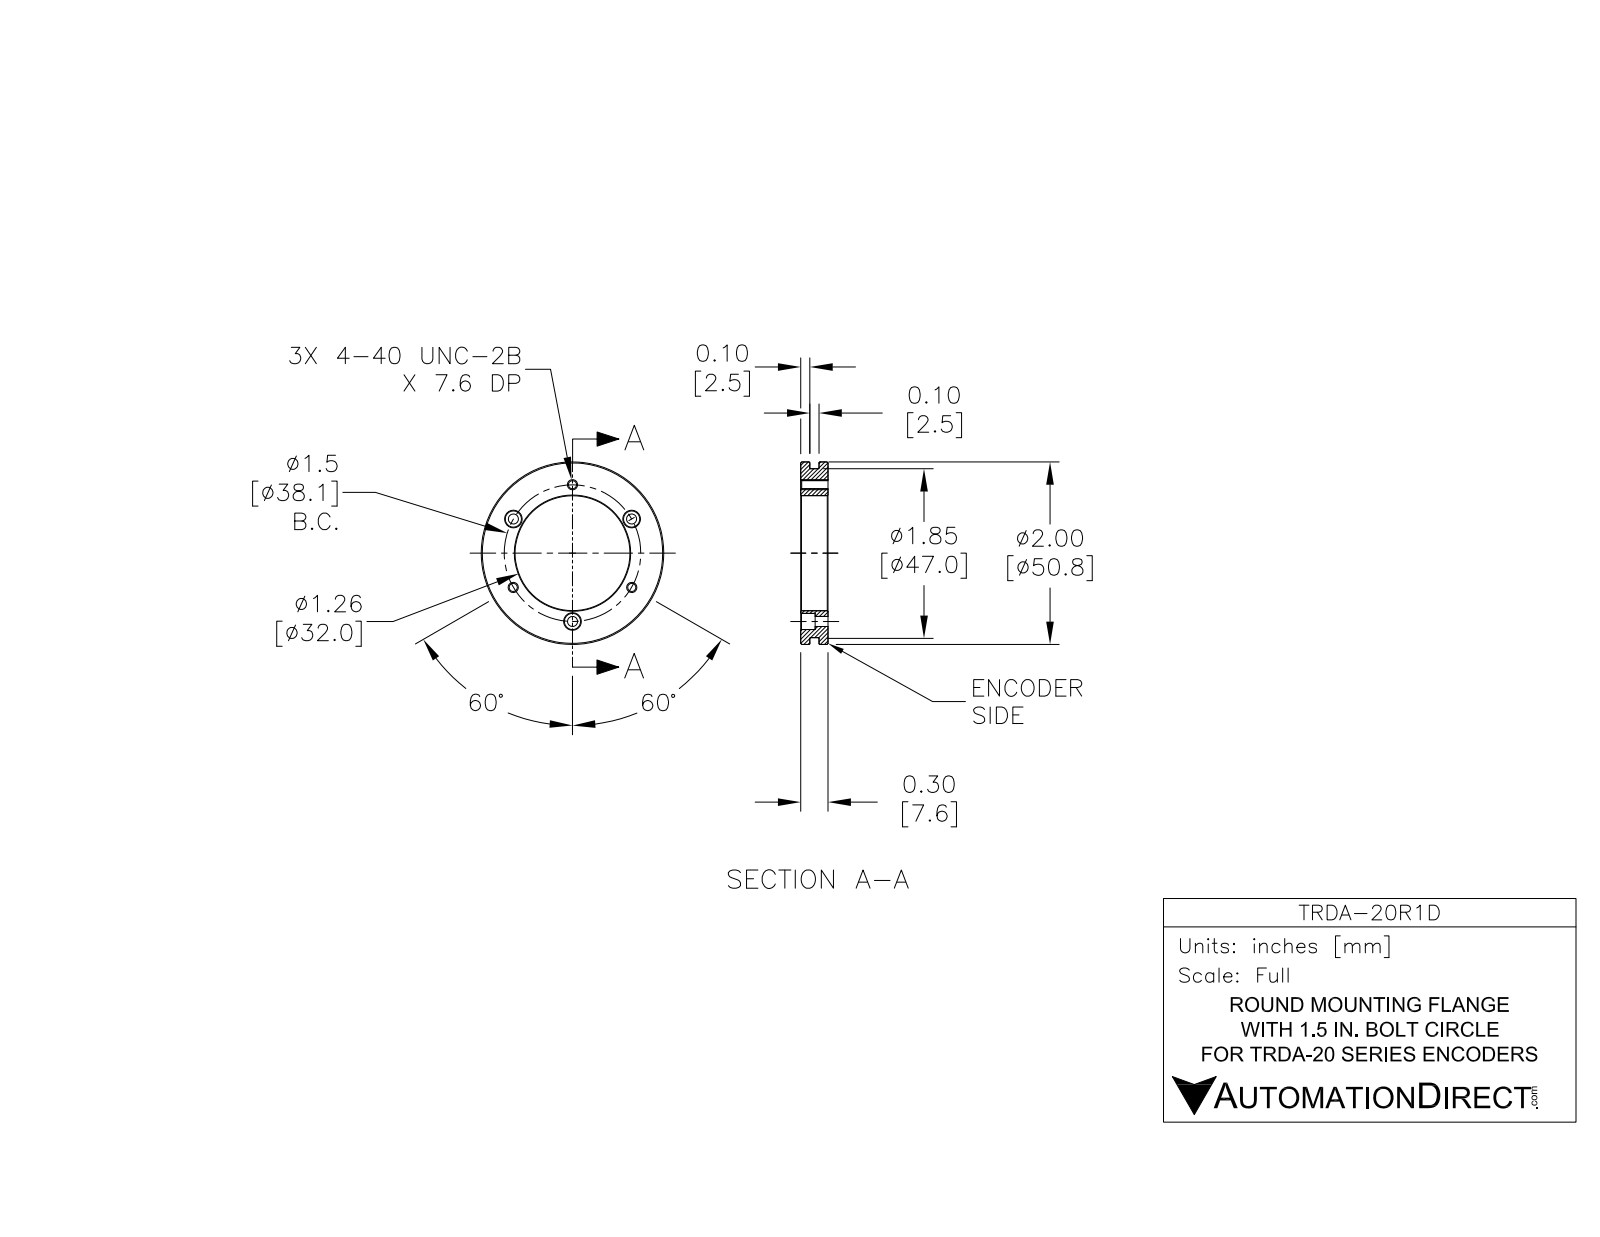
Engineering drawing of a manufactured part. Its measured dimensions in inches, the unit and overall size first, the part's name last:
Units: inches
Overall size (bounding box): 2 × 2 × 0.299
Round holes (diameter × count): ⌀0.089 ×3, ⌀0.11 ×3, ⌀0.177 ×3, ⌀1.26 ×1
Round bosses / shafts (diameter × count): ⌀0.11 ×3, ⌀2 ×1, ⌀1.85 ×1
Main face-to-face distances: 0.299, 0.1, 0.199, 0.099, 0.2, 0.142, 0.043, 0.057, 0.157, 0.298
Hole centre spacings: 0.749, 0.748, 0.75, 1.299, 1.498, 0.749, 1.296, 1.295
Volume: 0.508 in³ · Surface area: 8.41 in²
Bodies: 4 solids, 73 faces (13 planar, 32 cylindrical, 28 other)
Part name (STEP PRODUCT): TRDA-20R1D
STEP written by: SolidWorks 2017 (AUTOMOTIVE_DESIGN)
